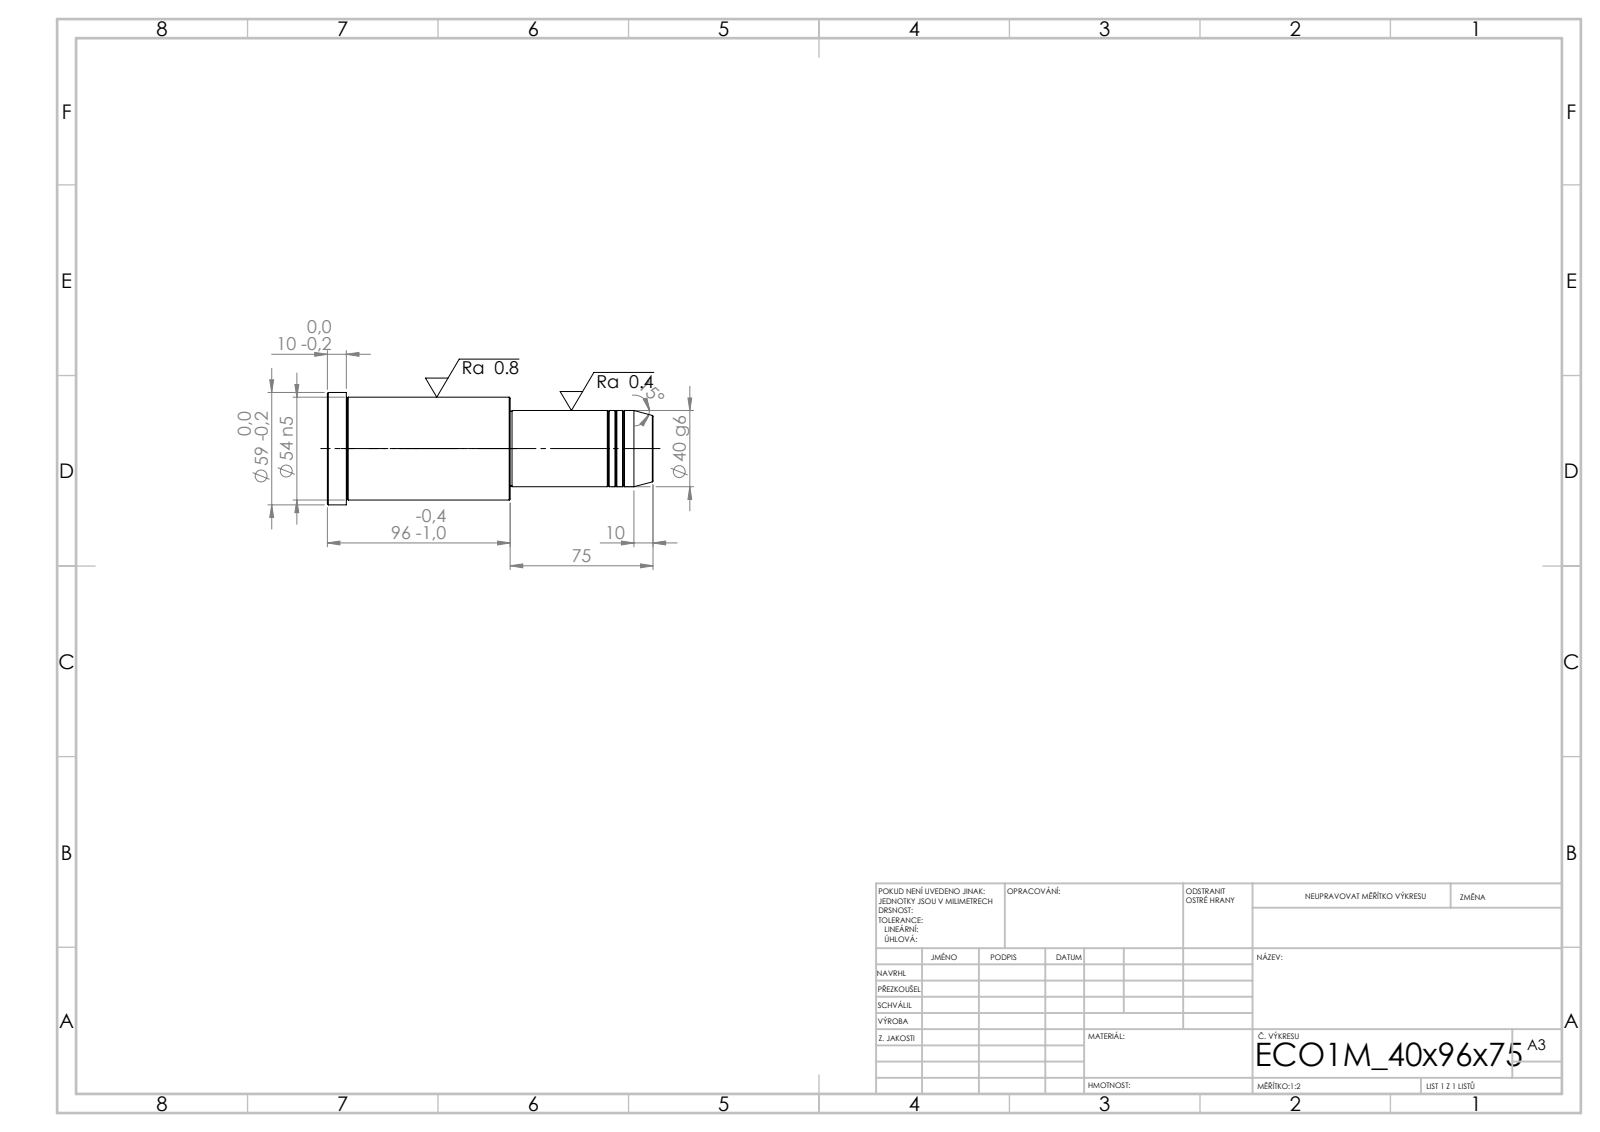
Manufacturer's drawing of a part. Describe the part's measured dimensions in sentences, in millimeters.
Its 3-D file was written by "SolidWorks 2019 (CONFIG_CONTROL_DESIGN)". It is 1 solid with 43 faces: 5 planar, 14 cylindrical and 24 other. Overall it measures 171 by 59 by 59 millimeters. Its volume is 316 616 cubic millimeters and its surface area 31 282 square millimeters. Round bosses or shafts: 1 of diameter 59, 1 of diameter 54, 1 of diameter 40, 1 of diameter 39. The main face-to-face distances are 96, 75, 171, 161, 86, 10, 74, 1, 87, 97.
